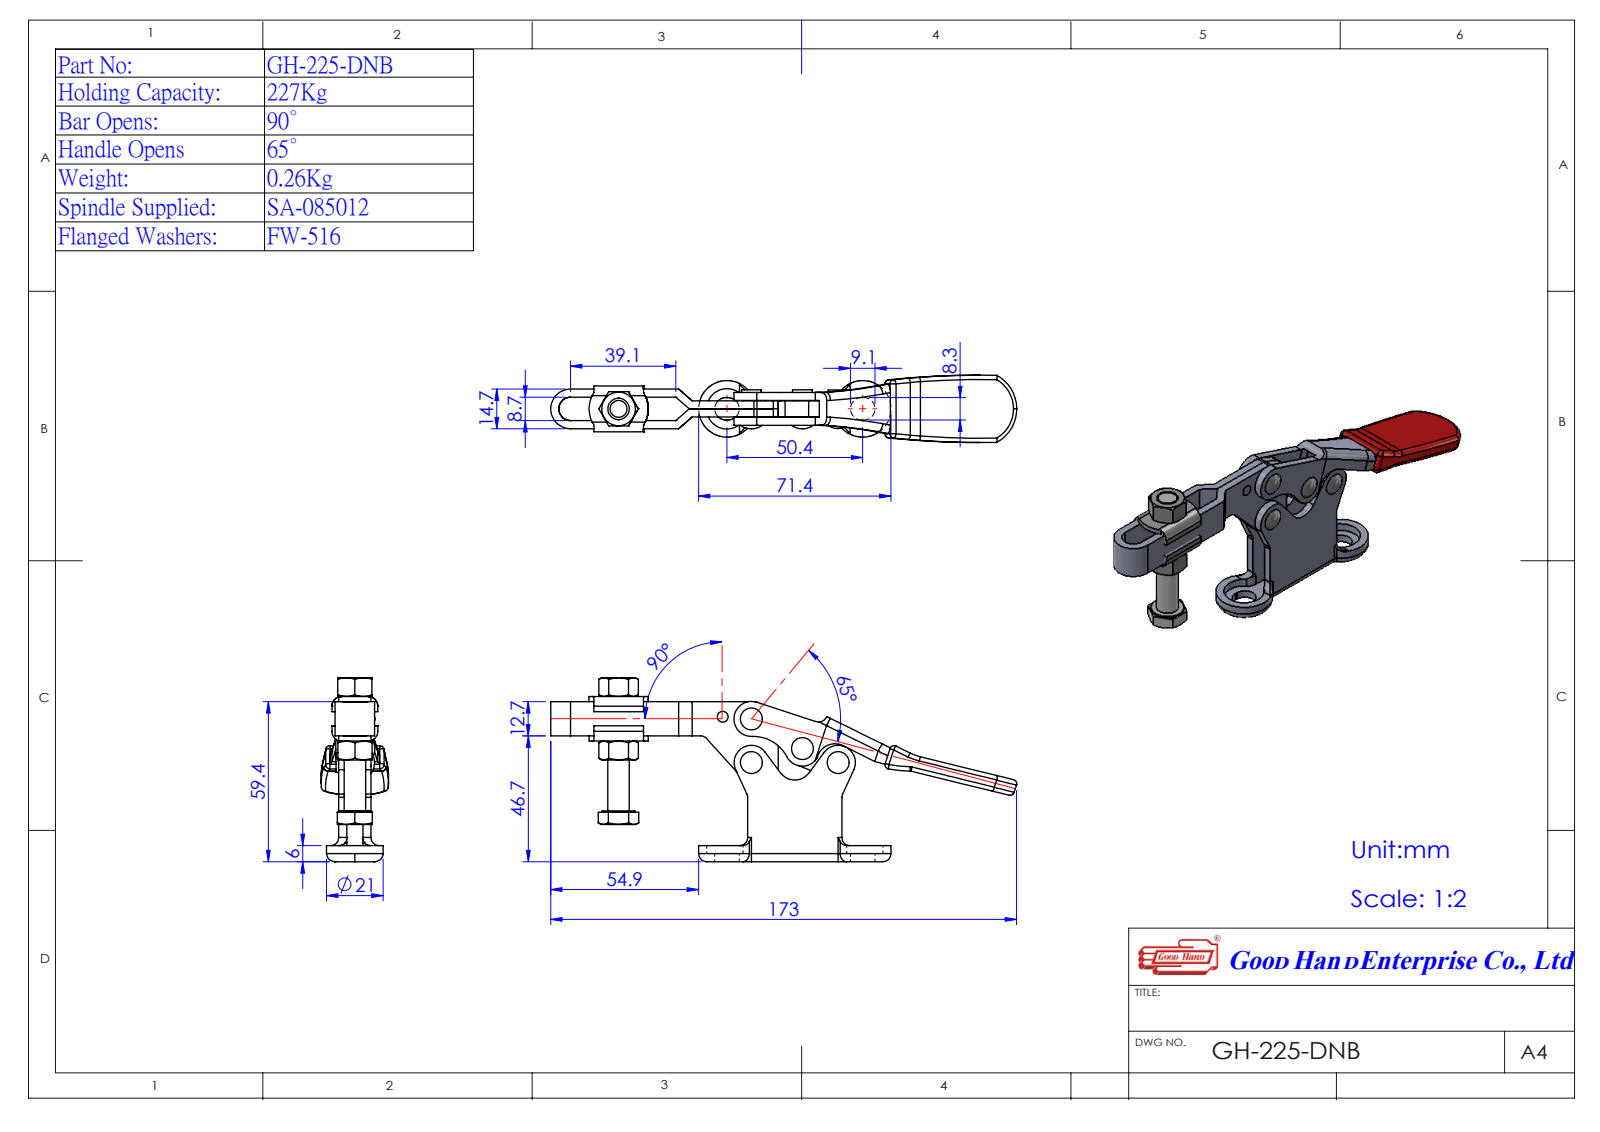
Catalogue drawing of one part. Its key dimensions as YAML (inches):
part_name: "Group2^GH-225-DNB(簡化); GH-225-DNB(簡化)-1; Group1^GH-225-DNB(簡化); 1225D05-1^GH-225-DNB(簡化)-1 (+2 more)"
step_written_by: "SolidWorks 2016 (AUTOMOTIVE_DESIGN)"
units: inches
bodies: {solids: 4, faces: 307, planar: 122, cylindrical: 145, other: 40}
overall_size: [6.833, 2.821, 0.984]
volume: 1.705
surface_area: 44.01
round_holes:
  - {diameter: 0.197, count: 4}
round_bosses_or_shafts:
  - {diameter: 0.289, count: 4}
  - {diameter: 0.25, count: 2}
  - {diameter: 0.248, count: 2}
  - {diameter: 0.492, count: 1}
  - {diameter: 0.315, count: 1}
  - {diameter: 0.157, count: 1}
partial_cylinders:
  - {radius: 0.118, count: 13}
  - {radius: 0.047, count: 4}
  - {radius: 0.142, count: 4}
  - {radius: 0.435, count: 4}
  - {radius: 0.252, count: 3}
  - {radius: 0.256, count: 3}
  - {radius: 0.039, count: 2}
  - {radius: 0.039, count: 2}
face_to_face_distances: [0.118, 0.236, 0.354, 0.122, 0.24, 0.358, 0.119, 0.118, 0.237, 0.472]
hole_center_spacings: [0.561, 0.638, 0.773, 0.862, 1.268, 1.419]
